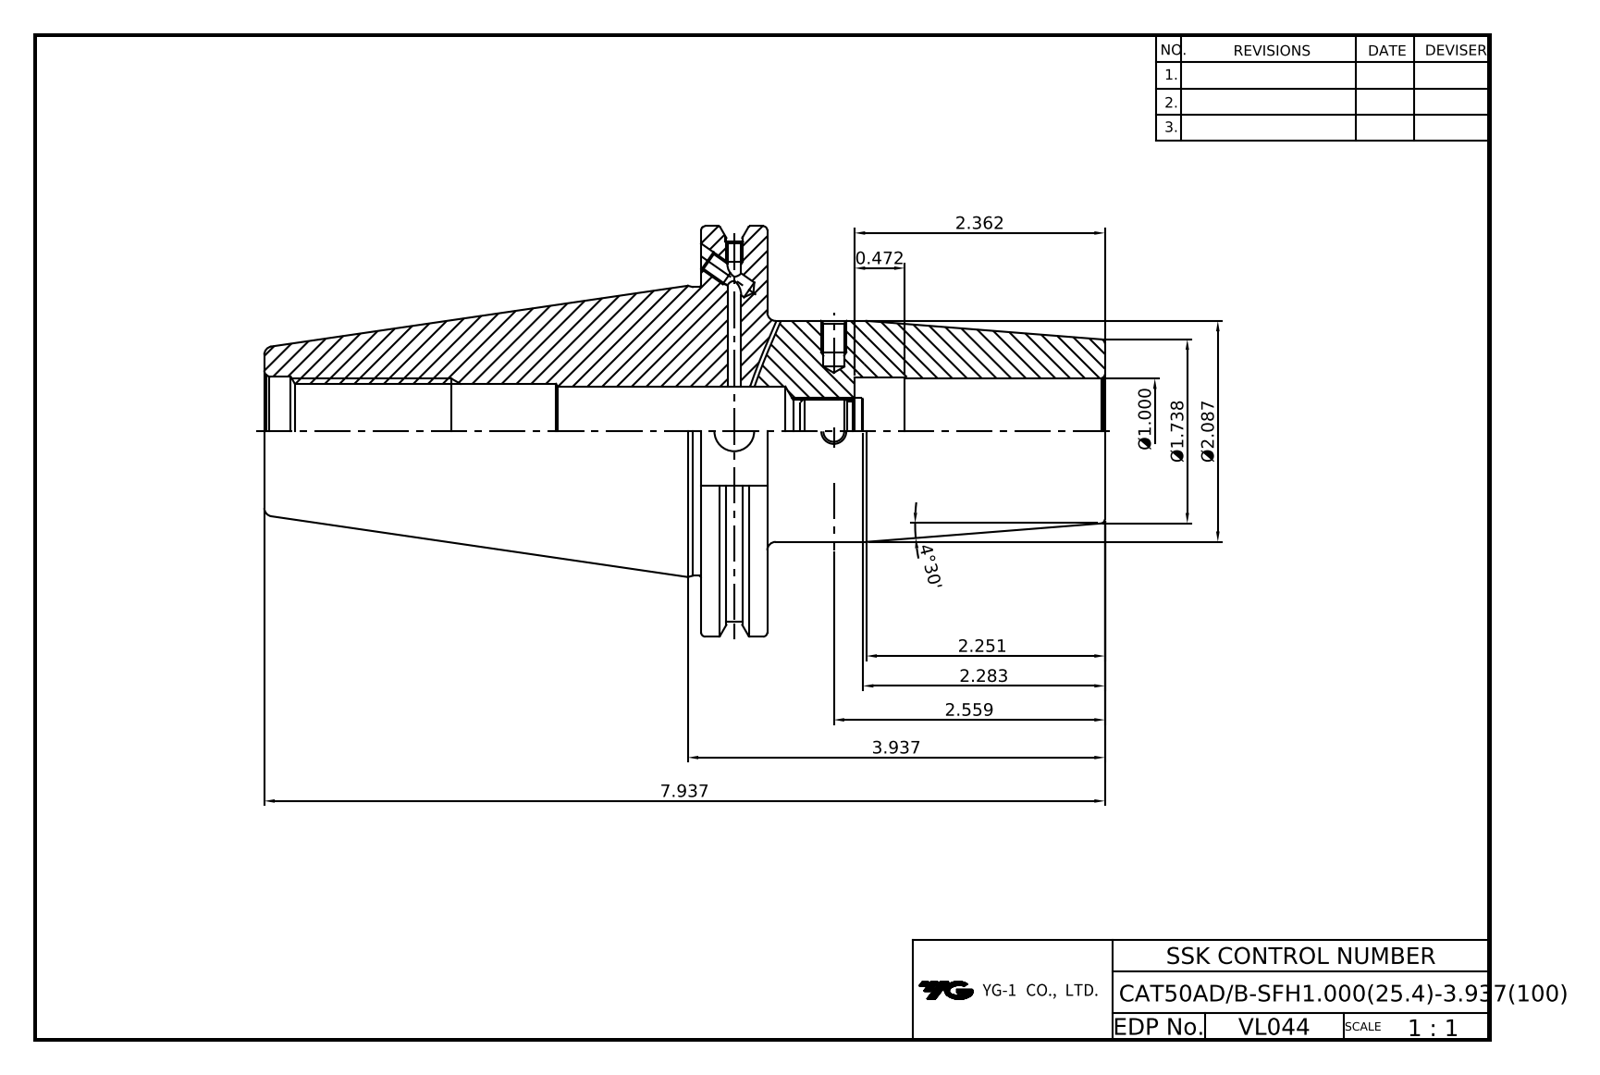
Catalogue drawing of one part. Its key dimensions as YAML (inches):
part_name: "LO-CAT50ADB-SFH25.4-100"
step_written_by: "Autodesk Inventor 2025 (AUTOMOTIVE_DESIGN)"
units: inches
bodies: {solids: 1, faces: 84, planar: 37, cylindrical: 26, other: 21}
overall_size: [7.937, 3.875, 3.728]
volume: 27
surface_area: 97.05
round_holes:
  - {diameter: 0.128, count: 2}
  - {diameter: 0.163, count: 2}
  - {diameter: 0.165, count: 2}
  - {diameter: 0.197, count: 2}
  - {diameter: 0.375, count: 1}
  - {diameter: 0.587, count: 1}
  - {diameter: 0.865, count: 1}
  - {diameter: 1, count: 1}
  - {diameter: 1.031, count: 1}
  - {diameter: 1.047, count: 1}
round_bosses_or_shafts:
  - {diameter: 3.875, count: 1}
  - {diameter: 3.594, count: 1}
  - {diameter: 2.726, count: 1}
  - {diameter: 2.087, count: 1}
face_to_face_distances: [0.625, 3.812, 3.187, 4.125, 4.75, 7.937, 5.575, 1.45, 0.825, 2.362]
